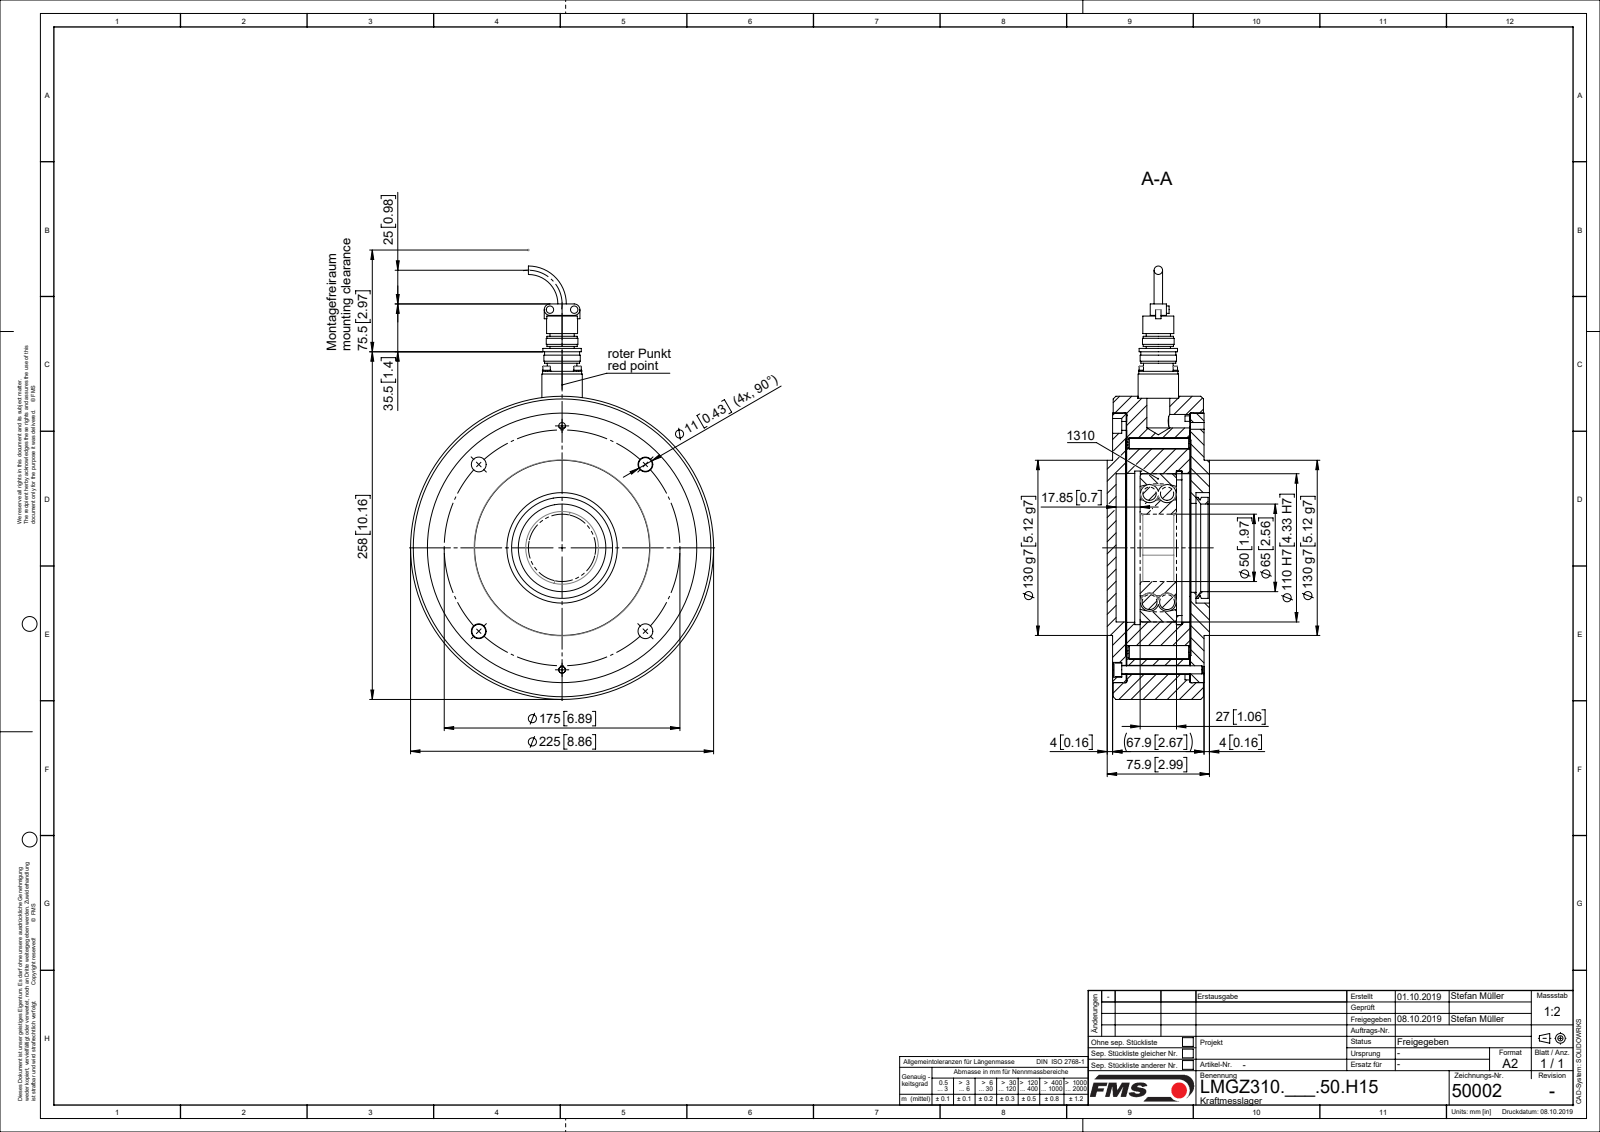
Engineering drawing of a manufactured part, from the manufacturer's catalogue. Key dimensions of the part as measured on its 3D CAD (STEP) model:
Part name (STEP PRODUCT): L50002; L49152; TEIL1; L49151 (+8 more)
STEP written by: Mechanical Desktop 2007 (CONFIG_CONTROL_DESIGN)
Units: millimetres
Bodies: 19 solids, 385 faces (109 planar, 226 cylindrical, 50 other)
Overall size (bounding box): 321.65 × 225 × 75.9
Volume: 2 405 000 mm³ · Surface area: 388 586 mm²
Round holes (diameter × count): ⌀11 ×6, ⌀2.6 ×4, ⌀3.2 ×4, ⌀3.4 ×4, ⌀9 ×4, ⌀5 ×2, ⌀6.6 ×2, ⌀23 ×1, ⌀50 ×1, ⌀64 ×1, ⌀66 ×1, ⌀82 ×1
Round bosses / shafts (diameter × count): ⌀5.5 ×6, ⌀6.2 ×4, ⌀3 ×4, ⌀2.5 ×4, ⌀225 ×1, ⌀199 ×1, ⌀130 ×1, ⌀74 ×1
Partial cylindrical surfaces — rounded edges, fillets, slot ends (radius × count): R4.25 ×2, R81 ×1, R86 ×1
Main face-to-face distances: 9.7, 47.25, 10.45, 10.75, 47.45, 10.2, 57.45, 57.7, 47, 10
Hole centre spacings: 16.26, 23, 87.5, 32.53, 68.17, 68.18, 90.5, 123.74
